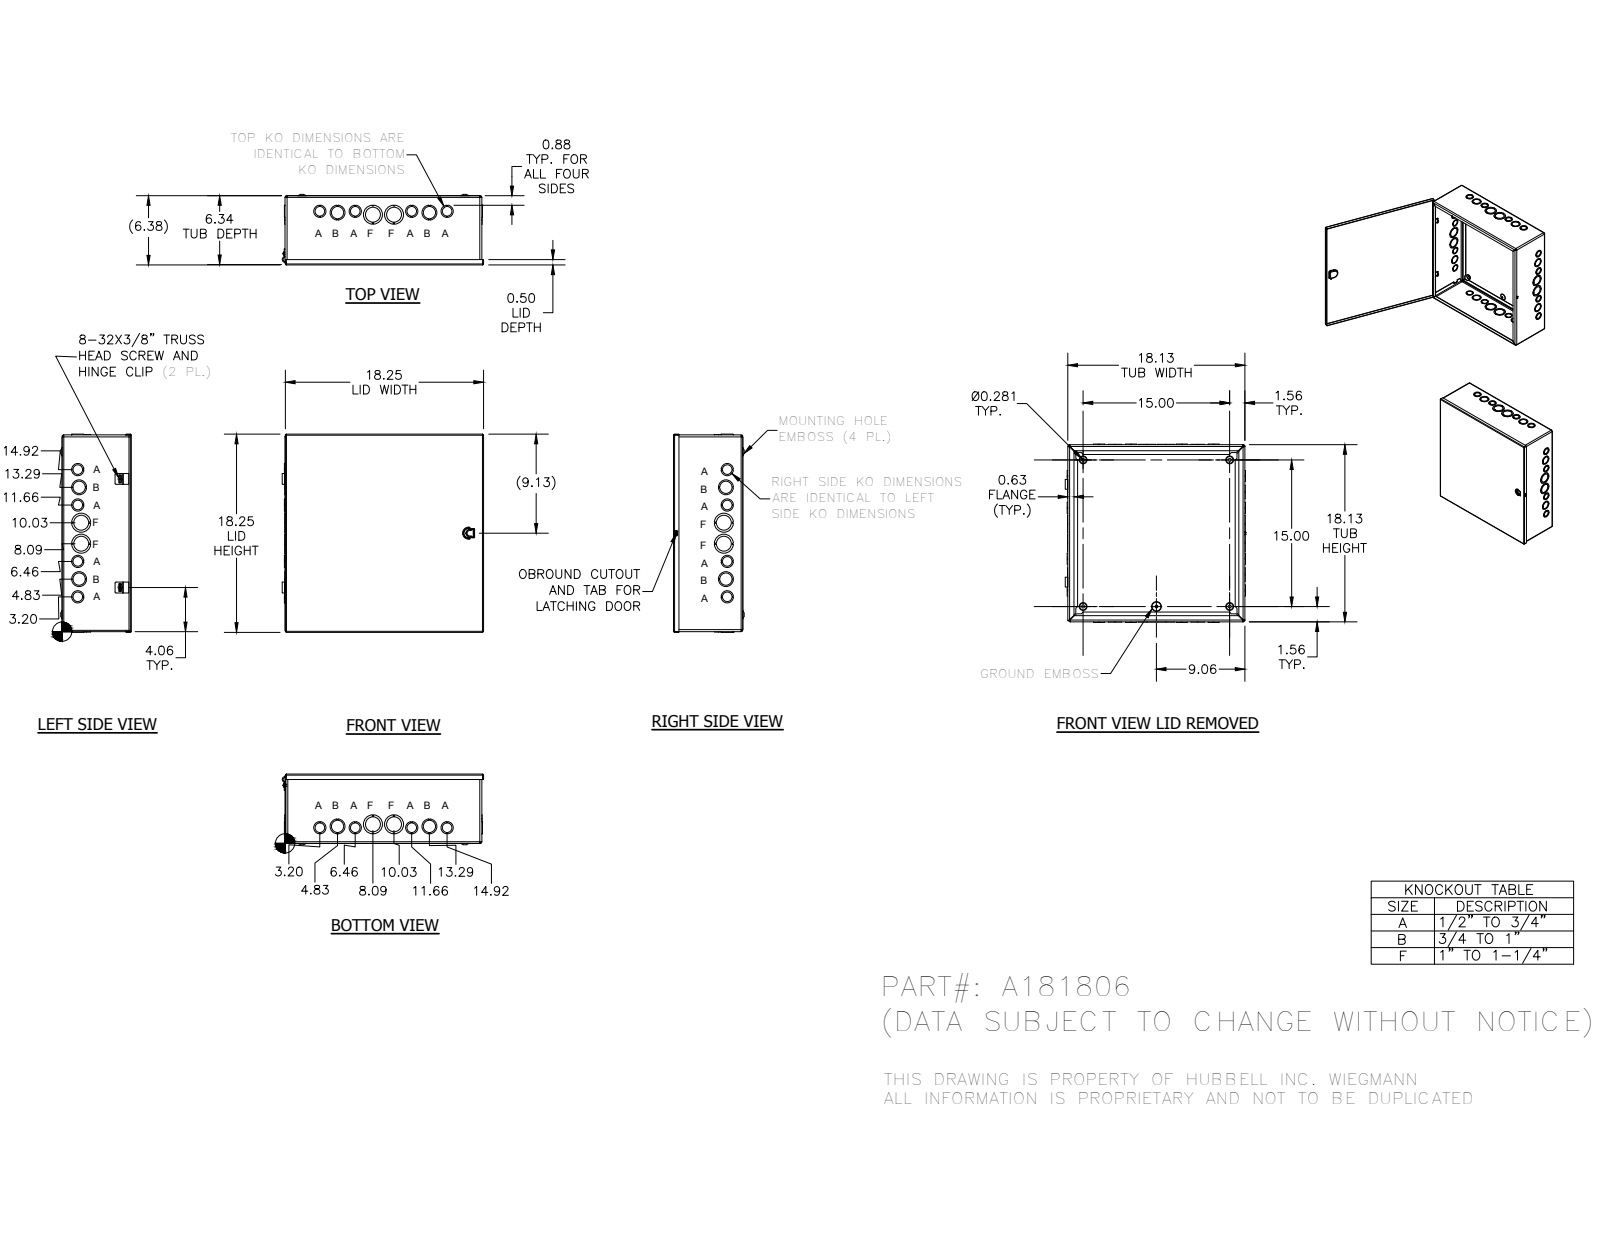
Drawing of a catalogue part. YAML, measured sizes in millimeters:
part_name: "A1818BA; A181806WRA; 31816; 372177 (+3 more)"
step_written_by: "Autodesk Inventor 2014 (AUTOMOTIVE_DESIGN)"
units: millimeters
bodies: {solids: 39, faces: 1391, planar: 934, cylindrical: 299, other: 158}
overall_size: [473.37, 468.29, 165.19]
round_holes:
  - {diameter: 28.57, count: 12}
  - {diameter: 22.22, count: 8}
  - {diameter: 34.92, count: 8}
  - {diameter: 7.62, count: 4}
  - {diameter: 44.45, count: 4}
  - {diameter: 3.56, count: 2}
  - {diameter: 4.19, count: 1}
round_bosses_or_shafts:
  - {diameter: 9.75, count: 2}
  - {diameter: 4.17, count: 2}
  - {diameter: 5.8, count: 1}
partial_cylinders:
  - {radius: 3.17, count: 15}
  - {radius: 0.79, count: 10}
  - {radius: 1.59, count: 9}
  - {radius: 2.38, count: 8}
  - {radius: 4.75, count: 8}
  - {radius: 1.4, count: 4}
  - {radius: 1.57, count: 4}
  - {radius: 1.78, count: 4}
face_to_face_distances: [1.58, 1.57, 160.43, 158.85, 458.8, 1.59, 160.44, 162.02, 457.23, 460.38]
hole_center_spacings: [41.52, 42.15, 82.94, 91.03, 132.17, 173.51, 214.88, 381]
